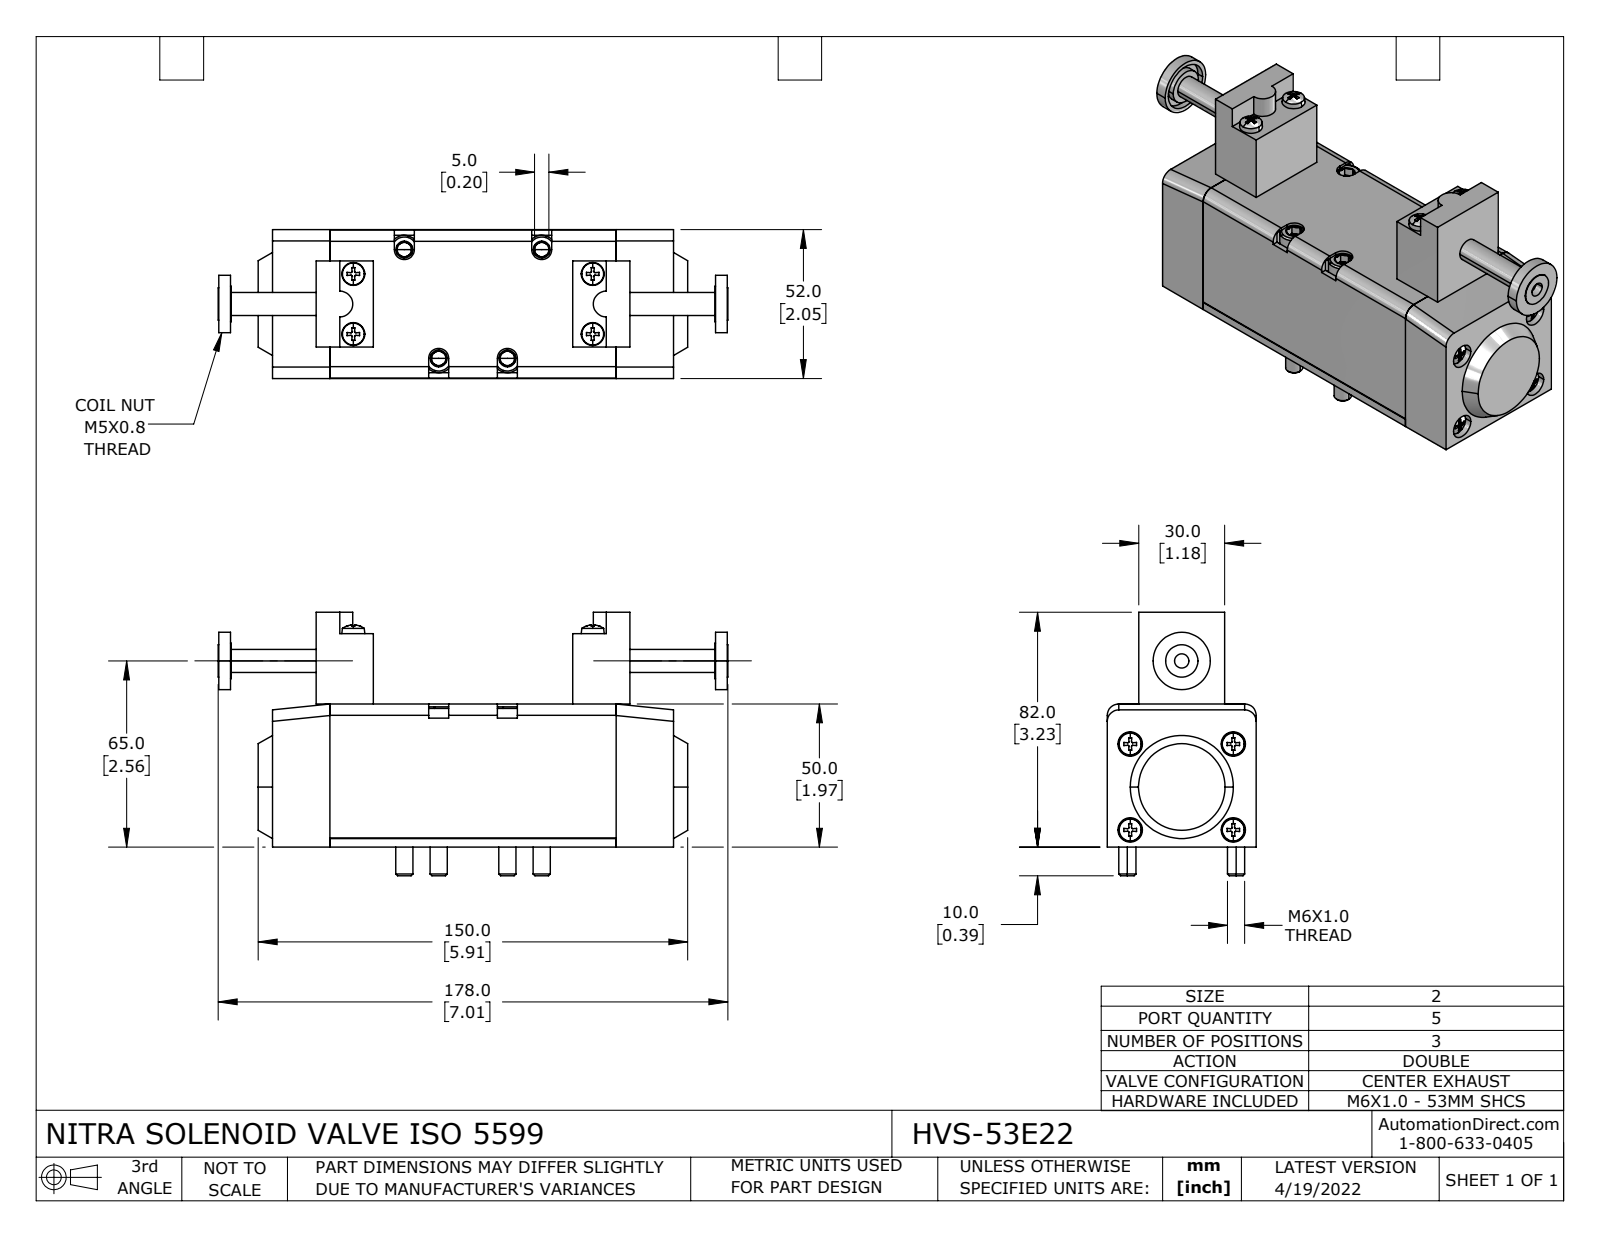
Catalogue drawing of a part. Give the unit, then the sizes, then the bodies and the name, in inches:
Units: inches
Overall size (bounding box): 7.008 × 3.622 × 2.047
Round holes (diameter × count): ⌀0.128 ×8, ⌀0.161 ×4, ⌀0.256 ×4, ⌀0.335 ×4, ⌀0.197 ×1, ⌀0.665 ×1
Round bosses / shafts (diameter × count): ⌀0.157 ×8, ⌀0.394 ×4, ⌀0.236 ×4, ⌀0.787 ×1, ⌀0.488 ×1, ⌀0.445 ×1, ⌀0.315 ×1
Partial cylindrical surfaces — rounded edges, fillets, slot ends (radius × count): R0.157 ×6, R0.138 ×4, R0.197 ×4, R0.177 ×2
Main face-to-face distances: 1.969, 3.937, 2.039, 2.043, 0.787, 0.598, 4.126, 4.724, 0.433, 1.614
Hole centre spacings: 0.777, 0.827, 1.181, 1.22, 1.344, 1.356, 1.417, 1.569
Volume: 24.75 in³ · Surface area: 119.3 in²
Bodies: 21 solids, 850 faces (434 planar, 156 cylindrical, 260 other)
Part name (STEP PRODUCT): HVS-53E22
STEP written by: SolidWorks 2021 (CONFIG_CONTROL_DESIGN)
